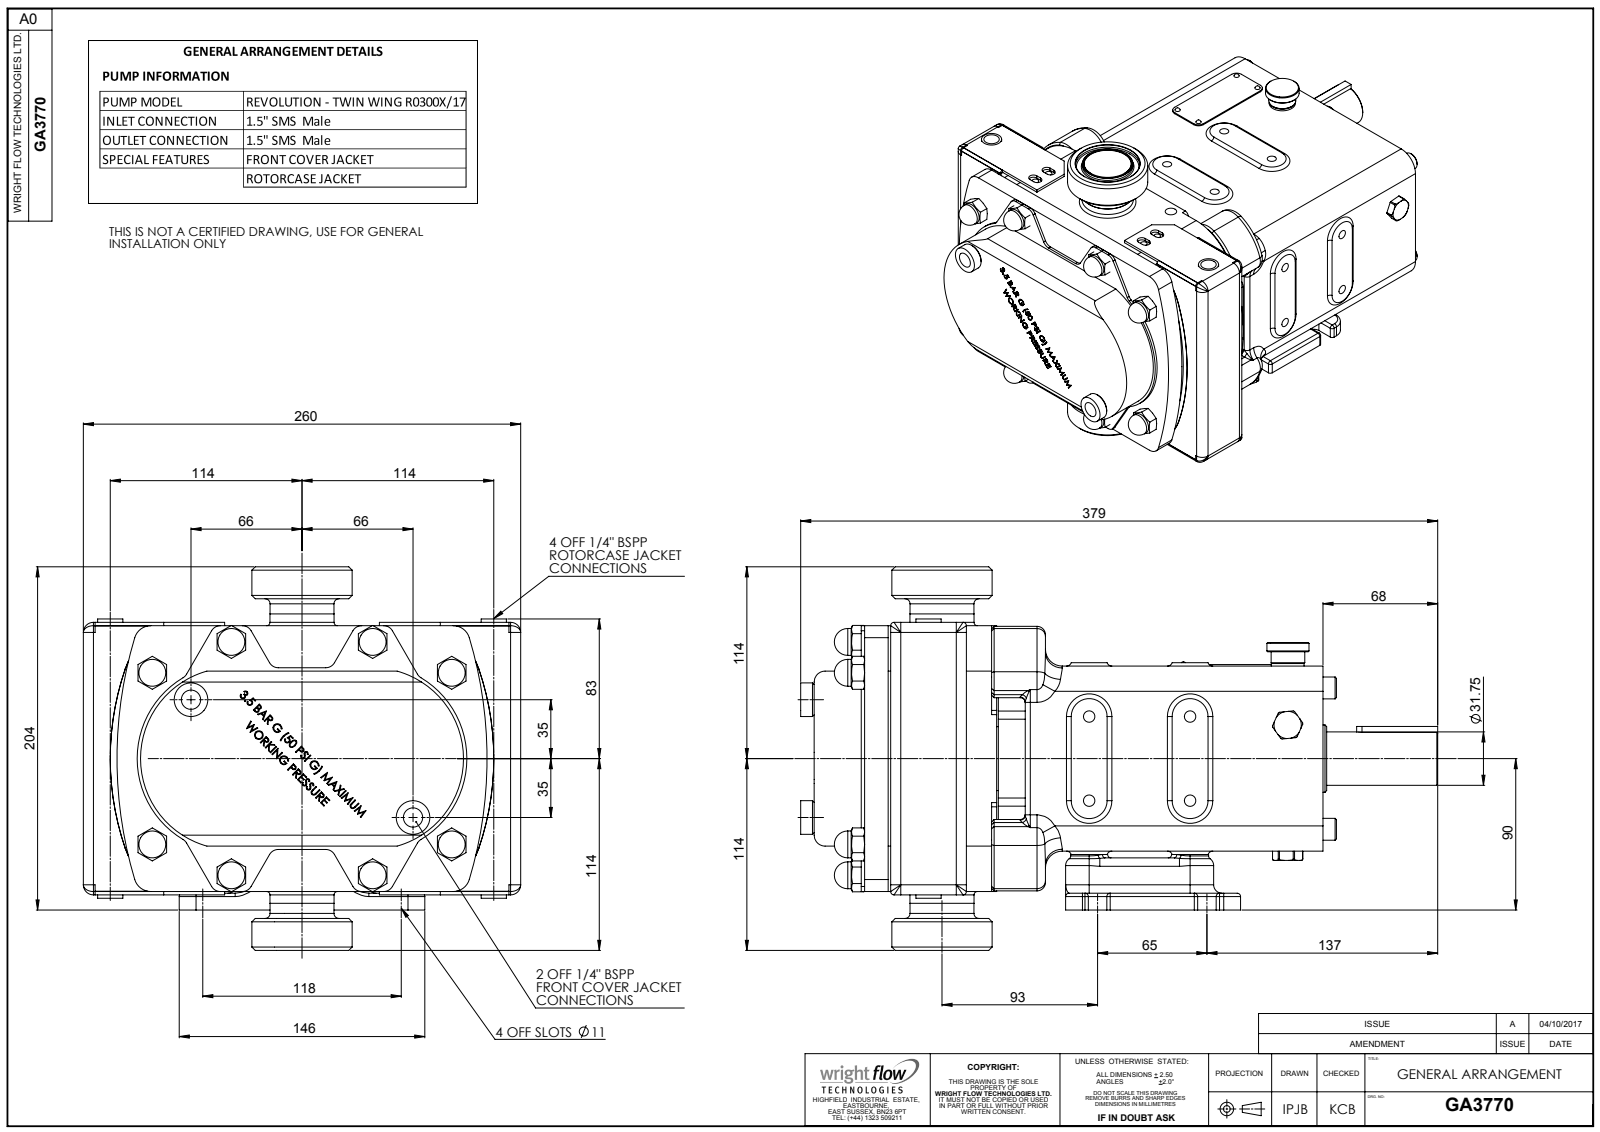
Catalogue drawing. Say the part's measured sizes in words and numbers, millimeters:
The part is named "Copy of Frame 3 Bolt on Jacket^GA3770; Copy of R0300 CPP V LHD^GA3770; Copy of Frame 3 Bolt on Jacket R-C^GA3770; GA3770 (+1 more)". Its 3-D file was written by "SolidWorks 2023 (AUTOMOTIVE_DESIGN)". It is 12 solids with 1819 faces: 774 planar, 471 cylindrical and 574 other. Overall it measures 378.7 by 260 by 228 millimeters. Its volume is 7 737 000 cubic millimeters and its surface area 558 409 square millimeters. Round holes: 8 of diameter 6.8, 4 of diameter 5, 4 of diameter 11.5, 4 of diameter 12, 2 of diameter 8.57, 1 of diameter 23, 1 of diameter 35, 1 of diameter 48. Round bosses or shafts: 8 of diameter 16, 7 of diameter 13, 5 of diameter 20, 2 of diameter 38, 2 of diameter 15, 1 of diameter 59.6, 1 of diameter 40, 1 of diameter 38.1. Partial cylindrical surfaces (rounded edges, fillets, slot ends): 30 of radius 10, 28 of radius 2, 28 of radius 3, 24 of radius 6, 19 of radius 5, 8 of radius 3.5, 8 of radius 4, 8 of radius 5.9. The main face-to-face distances are 2, 24, 134, 194, 1, 110, 78.5, 31, 272.5, 30. The hole center spacings are 50, 60, 78.1, 84, 14, 33.11, 41.9, 46.03.
